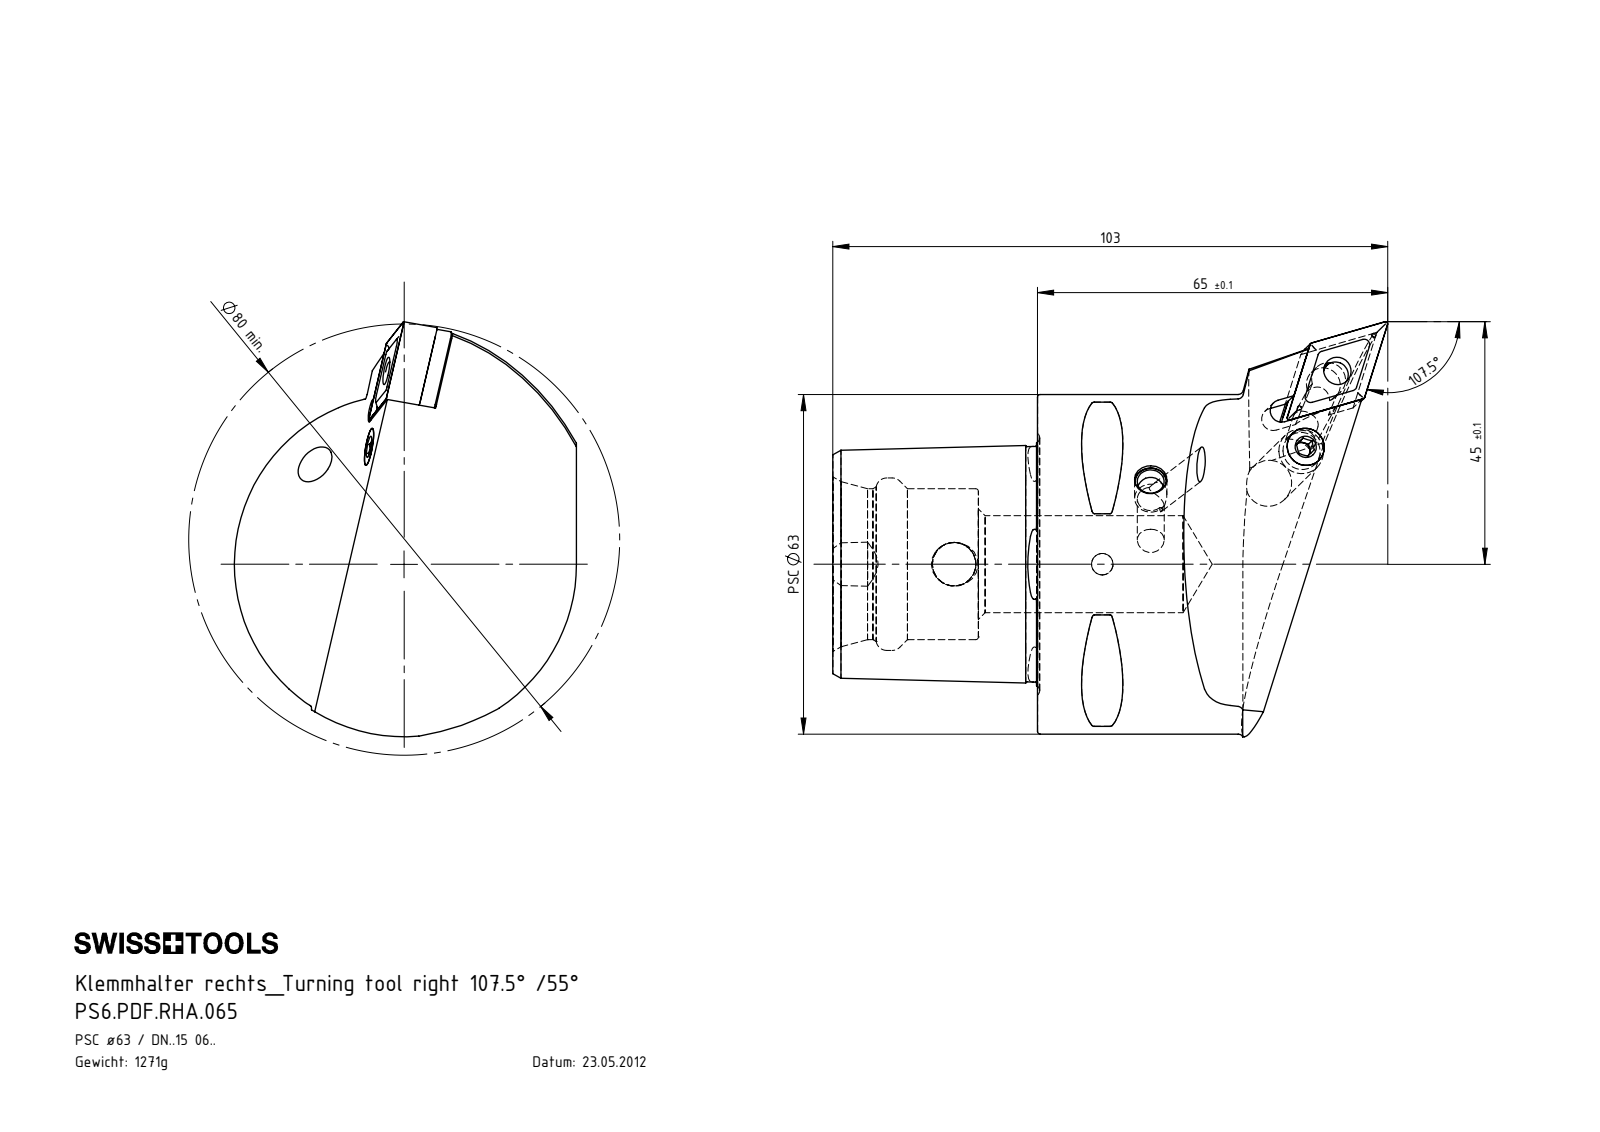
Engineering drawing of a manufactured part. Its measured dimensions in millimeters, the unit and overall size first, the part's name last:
Units: millimetres
Overall size (bounding box): 103 × 77 × 63.5
Round holes (diameter × count): ⌀5 ×2, ⌀4 ×1, ⌀5.16 ×1, ⌀6.4 ×1, ⌀7 ×1, ⌀8.1 ×1, ⌀8.4 ×1, ⌀18 ×1, ⌀28 ×1, ⌀32 ×1
Round bosses / shafts (diameter × count): ⌀63 ×1, ⌀8 ×1, ⌀7.9 ×1, ⌀6.4 ×1, ⌀6 ×1, ⌀4.7 ×1, ⌀3.55 ×1
Partial cylindrical surfaces — rounded edges, fillets, slot ends (radius × count): R0.5 ×8, R0.4 ×4, R1 ×4, R2.5 ×2, R6 ×2, R2.1 ×1, R2.35 ×1, R2.8 ×1
Main face-to-face distances: 38, 6.05, 24.88, 3.18, 9.23, 27, 11, 12.7, 12.32, 55.8
Hole centre spacings: 15.61, 27.5
Volume: 162 884 mm³ · Surface area: 31 015 mm²
Bodies: 8 solids, 335 faces (88 planar, 80 cylindrical, 167 other)
Part name (STEP PRODUCT): PS6-PDF.RHA.065; DNMG150604; WDF-ER2.101.003_A; WCD-ER1.101.000 (+4 more)
STEP written by: SolidWorks 2012 (CONFIG_CONTROL_DESIGN)
